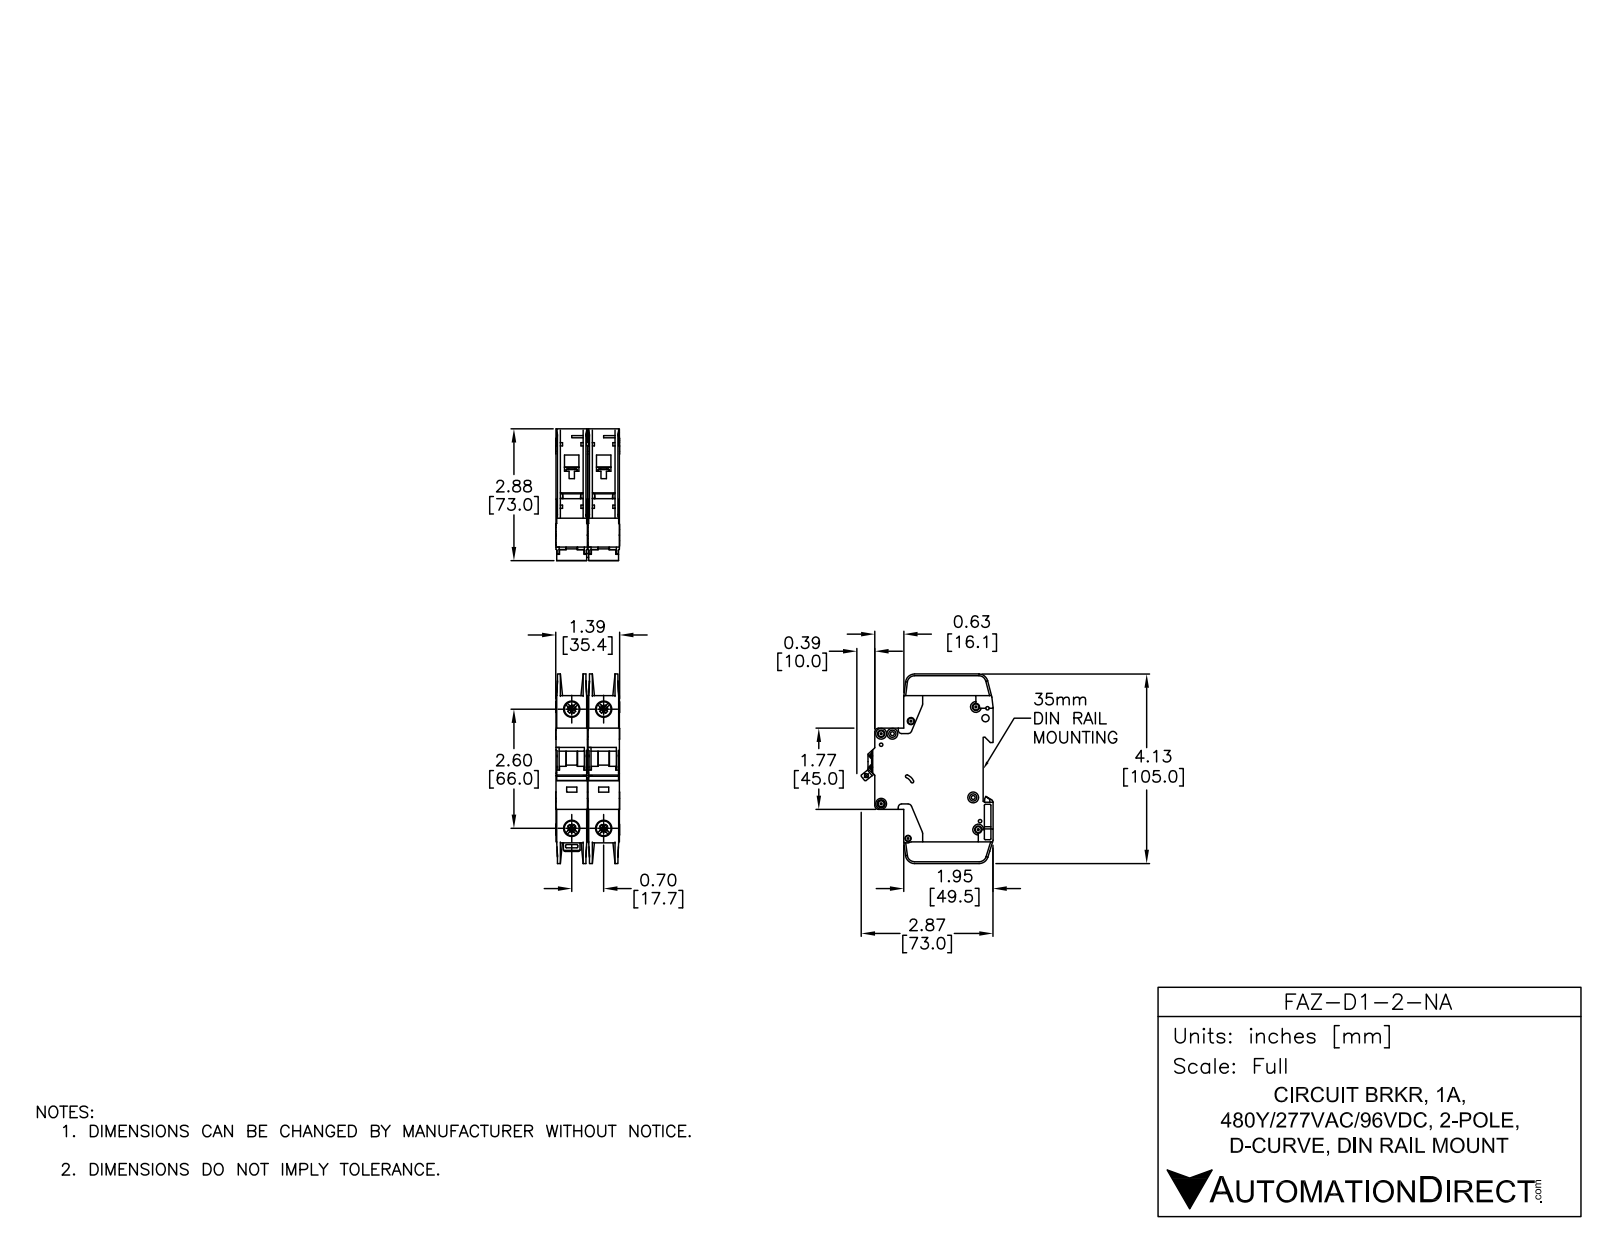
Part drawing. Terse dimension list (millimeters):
name: FAZ-D1-2-NA
written by: SolidWorks 2014 (AUTOMOTIVE_DESIGN)
unit: mm
bodies: 6 solids, 1568 faces (818 planar, 526 cylindrical, 224 other)
size: 105 × 73.04 × 35.4
volume: 155 390 mm³; area: 49 479 mm²
holes: 7× ⌀3.6, 4× ⌀7.15, 4× ⌀8.2, 2× ⌀1.09, 2× ⌀1.5, 2× ⌀4, 1× ⌀1.9, 1× ⌀2.15, 1× ⌀2.2, 1× ⌀2.55, 1× ⌀3.3, 1× ⌀3.4
bosses: 7× ⌀6, 2× ⌀2.5
rounds: 47× R0.25, 24× R0.5, 18× R1, 12× R2, 5× R5, 4× R1.8, 4× R4, 2× R0.2
face distances: 17.7, 17.5, 0.7, 15.05, 2.45, 1.75, 15.75, 13.3, 35.2, 17
hole spacings: 6.2, 17.7, 66, 68.33, 5.19, 6.1, 8.19, 8.56
